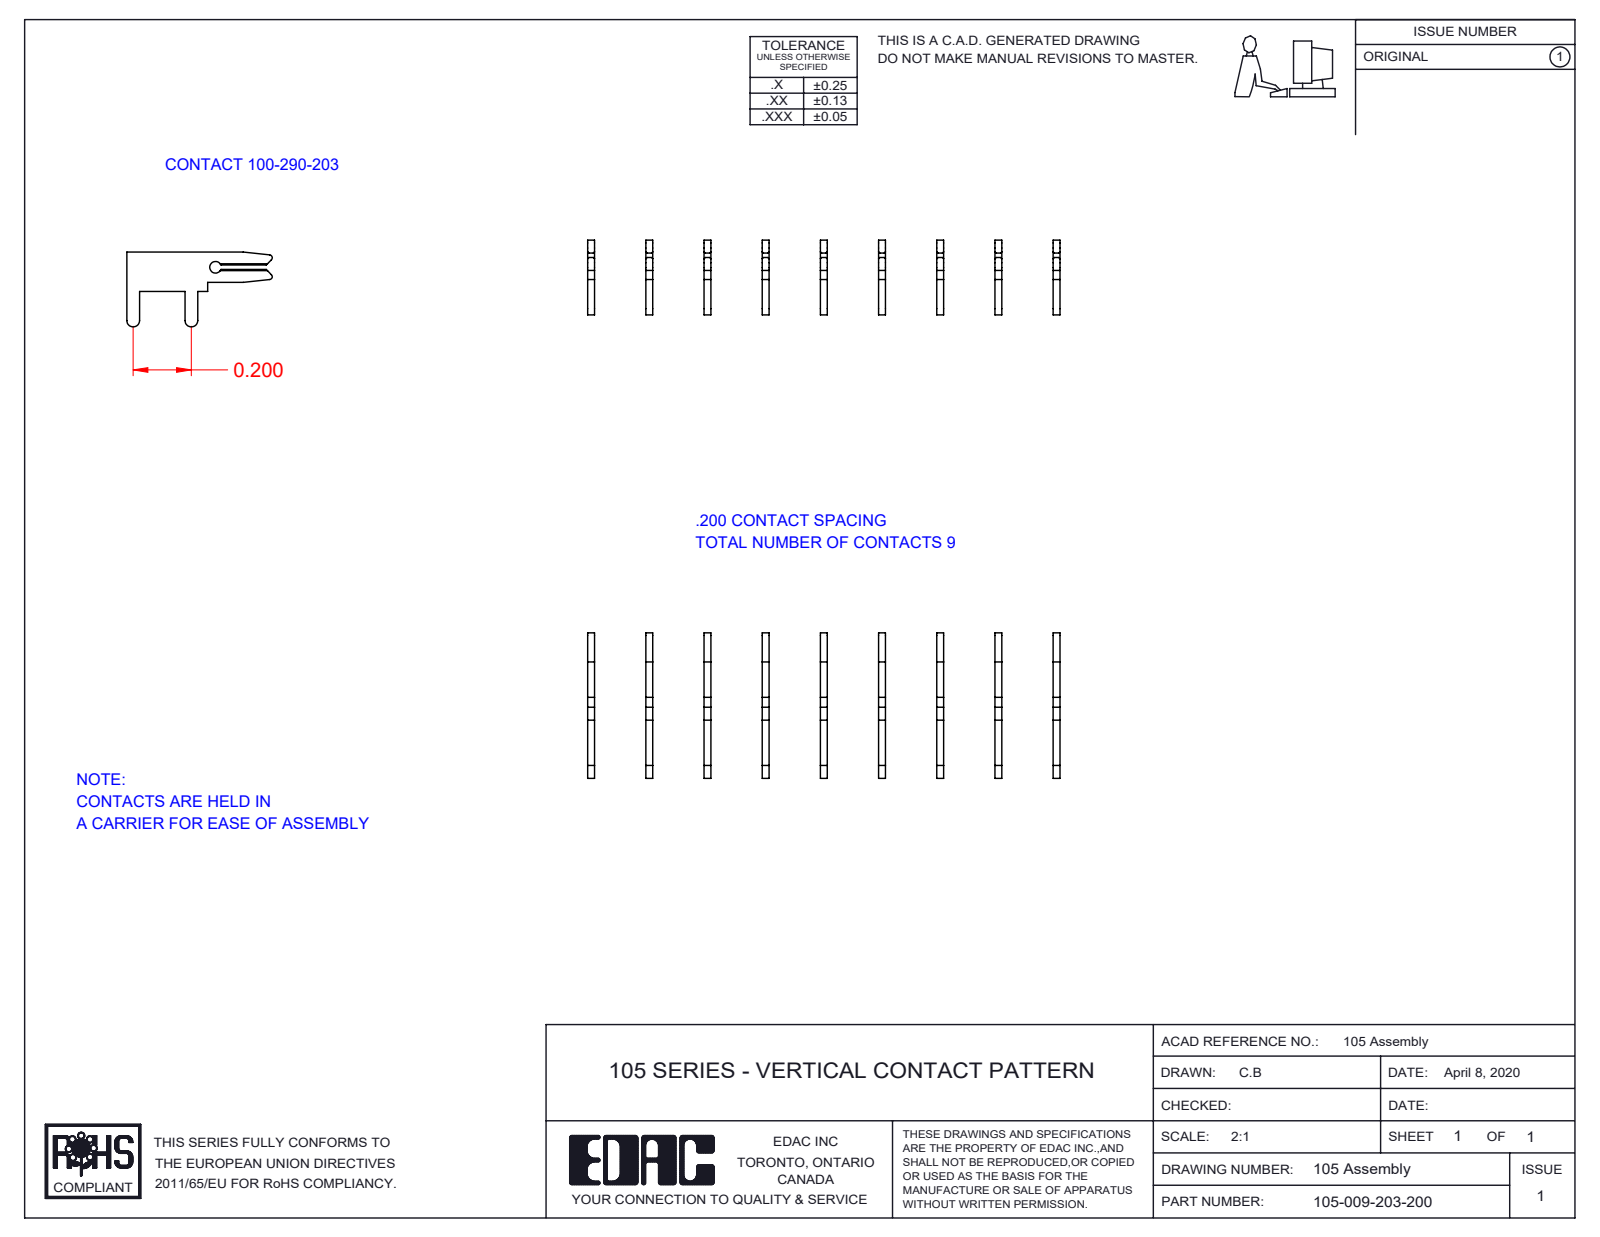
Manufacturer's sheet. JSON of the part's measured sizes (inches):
{"part_name": "105-009-203-200; 100-290-001_100-290-203", "step_written_by": "SolidWorks 2020 (CONFIG_CONTROL_DESIGN)", "units": "inches", "bodies": {"solids": 9, "faces": 252, "planar": 189, "cylindrical": 63, "other": 0}, "overall_size": [1.624, 0.5, 0.257], "volume_in3": 0.014, "surface_area_in2": 1.614, "round_holes": [[0.04, 1]], "partial_cylinders_radius": [[0.01, 2], [0.022, 2]], "face_to_face_distances": [0.2, 0.4, 0.6, 0.8, 0.024, 1, 0.224, 0.176, 0.424, 0.376]}
